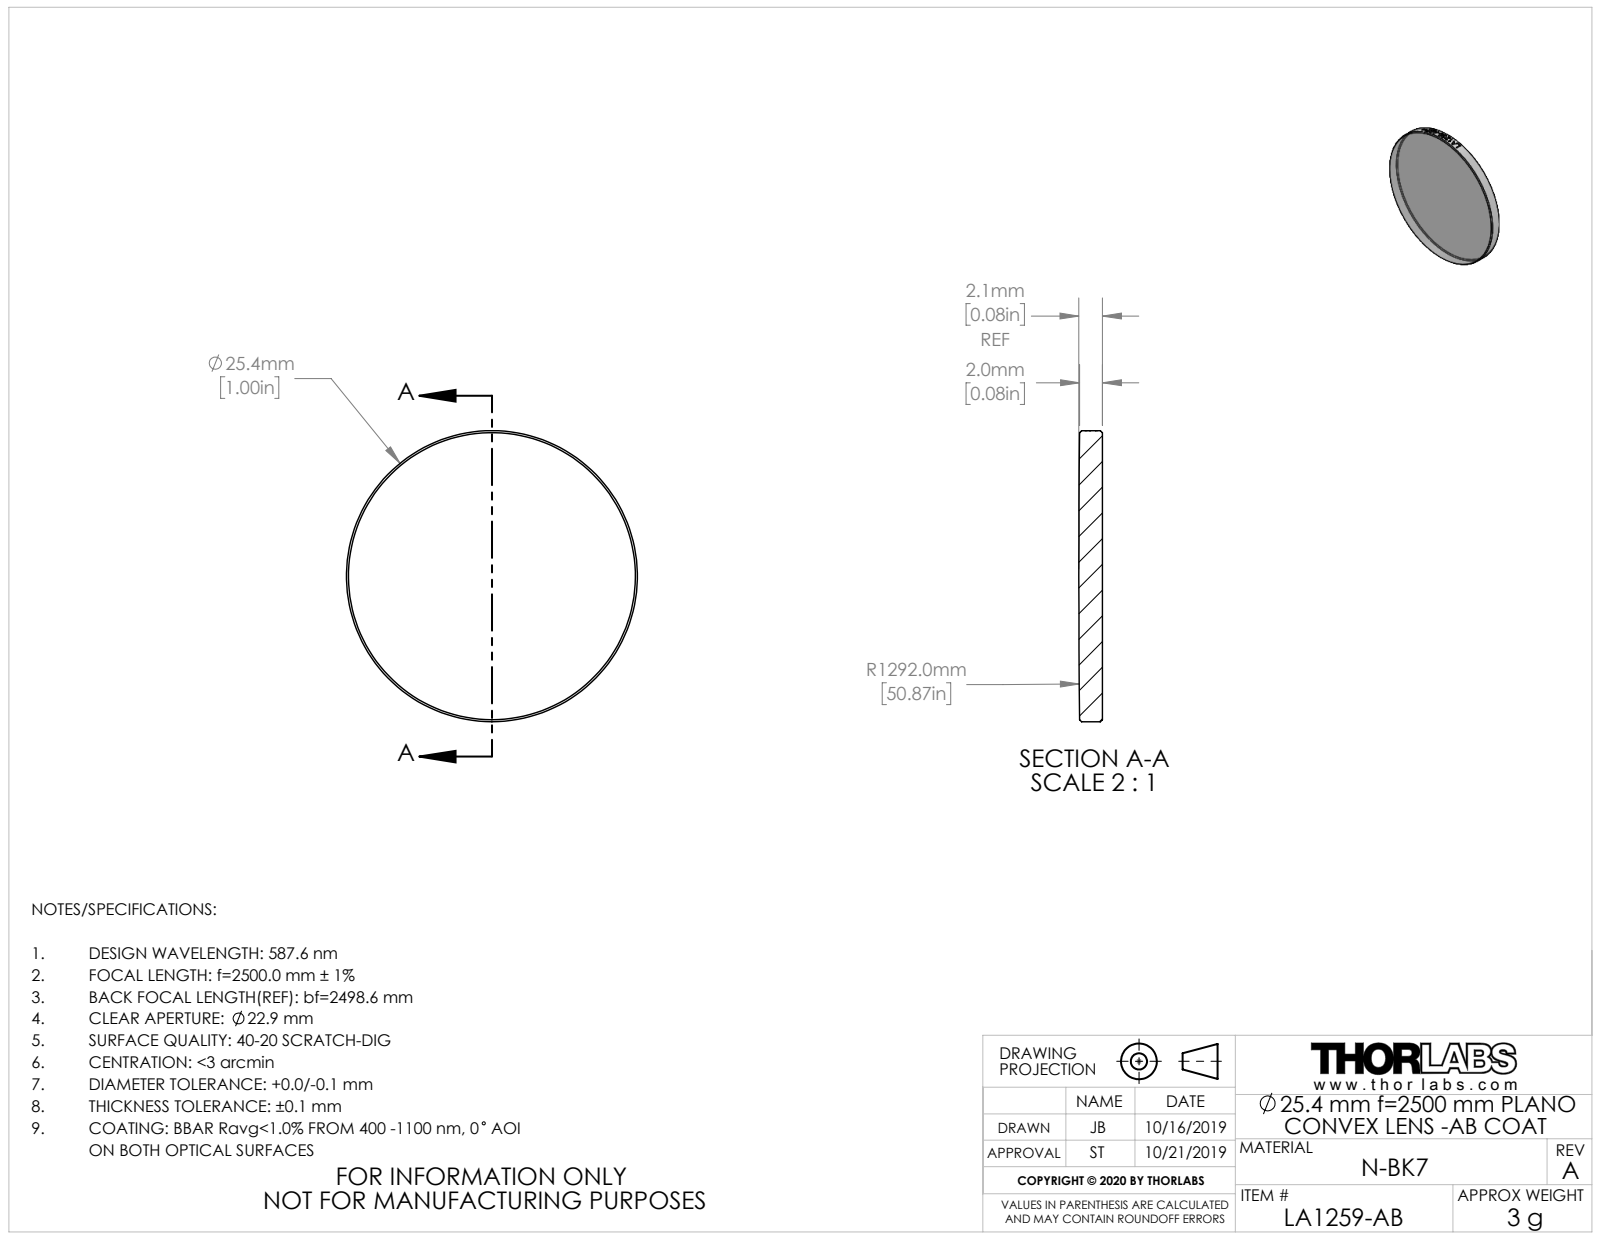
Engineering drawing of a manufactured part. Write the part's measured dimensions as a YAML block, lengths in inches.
part_name: "TTN195779-E0W"
step_written_by: "SolidWorks 2018 (CONFIG_CONTROL_DESIGN)"
units: inches
bodies: {solids: 1, faces: 29, planar: 1, cylindrical: 22, other: 6}
overall_size: [1, 1, 0.081]
volume: 0.063
surface_area: 1.792
round_bosses_or_shafts:
  - {diameter: 1, count: 1}
